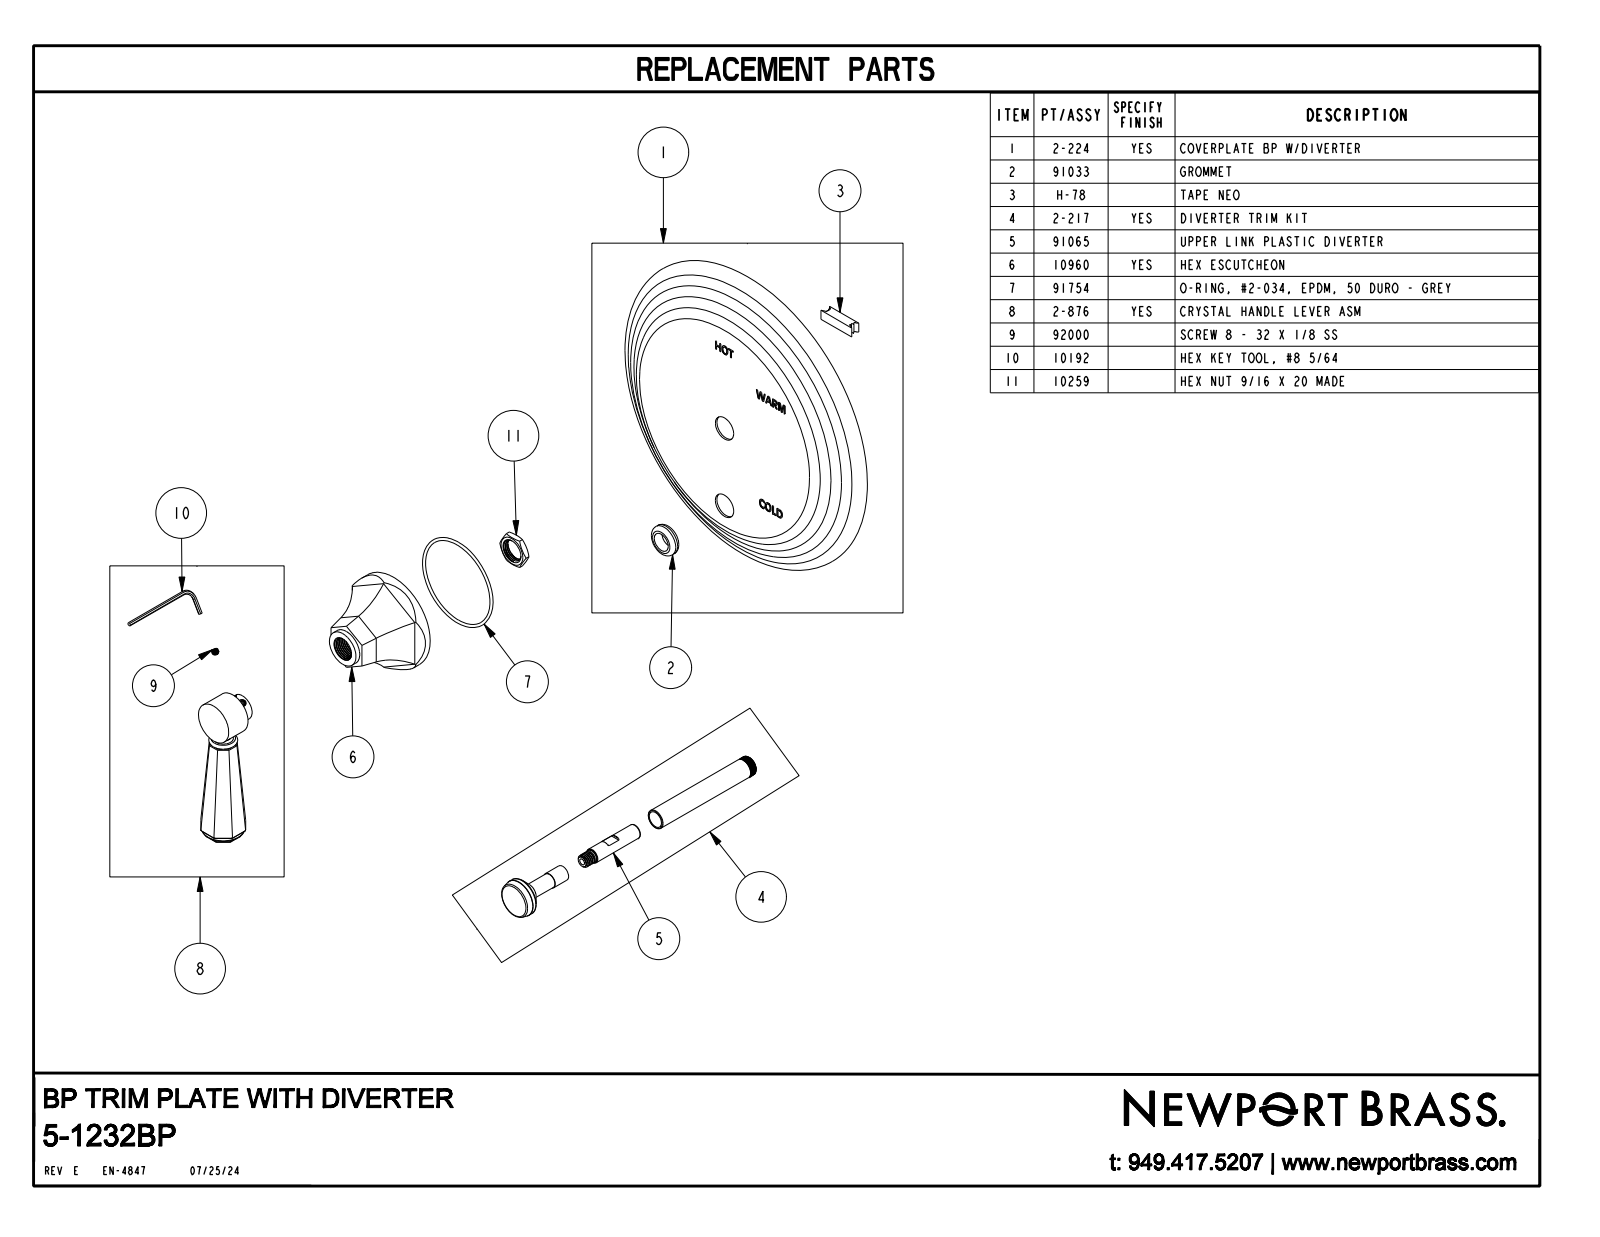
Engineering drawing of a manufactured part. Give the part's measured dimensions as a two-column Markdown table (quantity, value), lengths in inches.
| quantity | value |
| --- | --- |
| part name | 5-1232BP |
| STEP written by | CREO PARAMETRIC BY PTC INC, 2018400 (CONFIG_CONTROL_DESIGN) |
| units | inches |
| bodies | 1 solid, 331 faces (171 planar, 50 cylindrical, 110 other) |
| overall size | 7.75 × 7.75 × 3.537 |
| volume | 33.61 in³ |
| surface area | 122.5 in² |
| round holes (diameter × count) | 0.385 × 1 |
| round bosses / shafts (diameter × count) | 0.98 × 2, 2.375 × 1, 0.9 × 1, 0.86 × 1, 0.625 × 1, 0.472 × 1, 0.365 × 1, 0.354 × 1 |
| partial cylindrical surfaces (radius × count) | 0.03 × 24, 1.541 × 6 |
| main face-to-face distances | 0.754, 2.286, 1.532, 2.711, 1.957, 0.425, 2.281, 1.527, 0.43, 2.401 |
